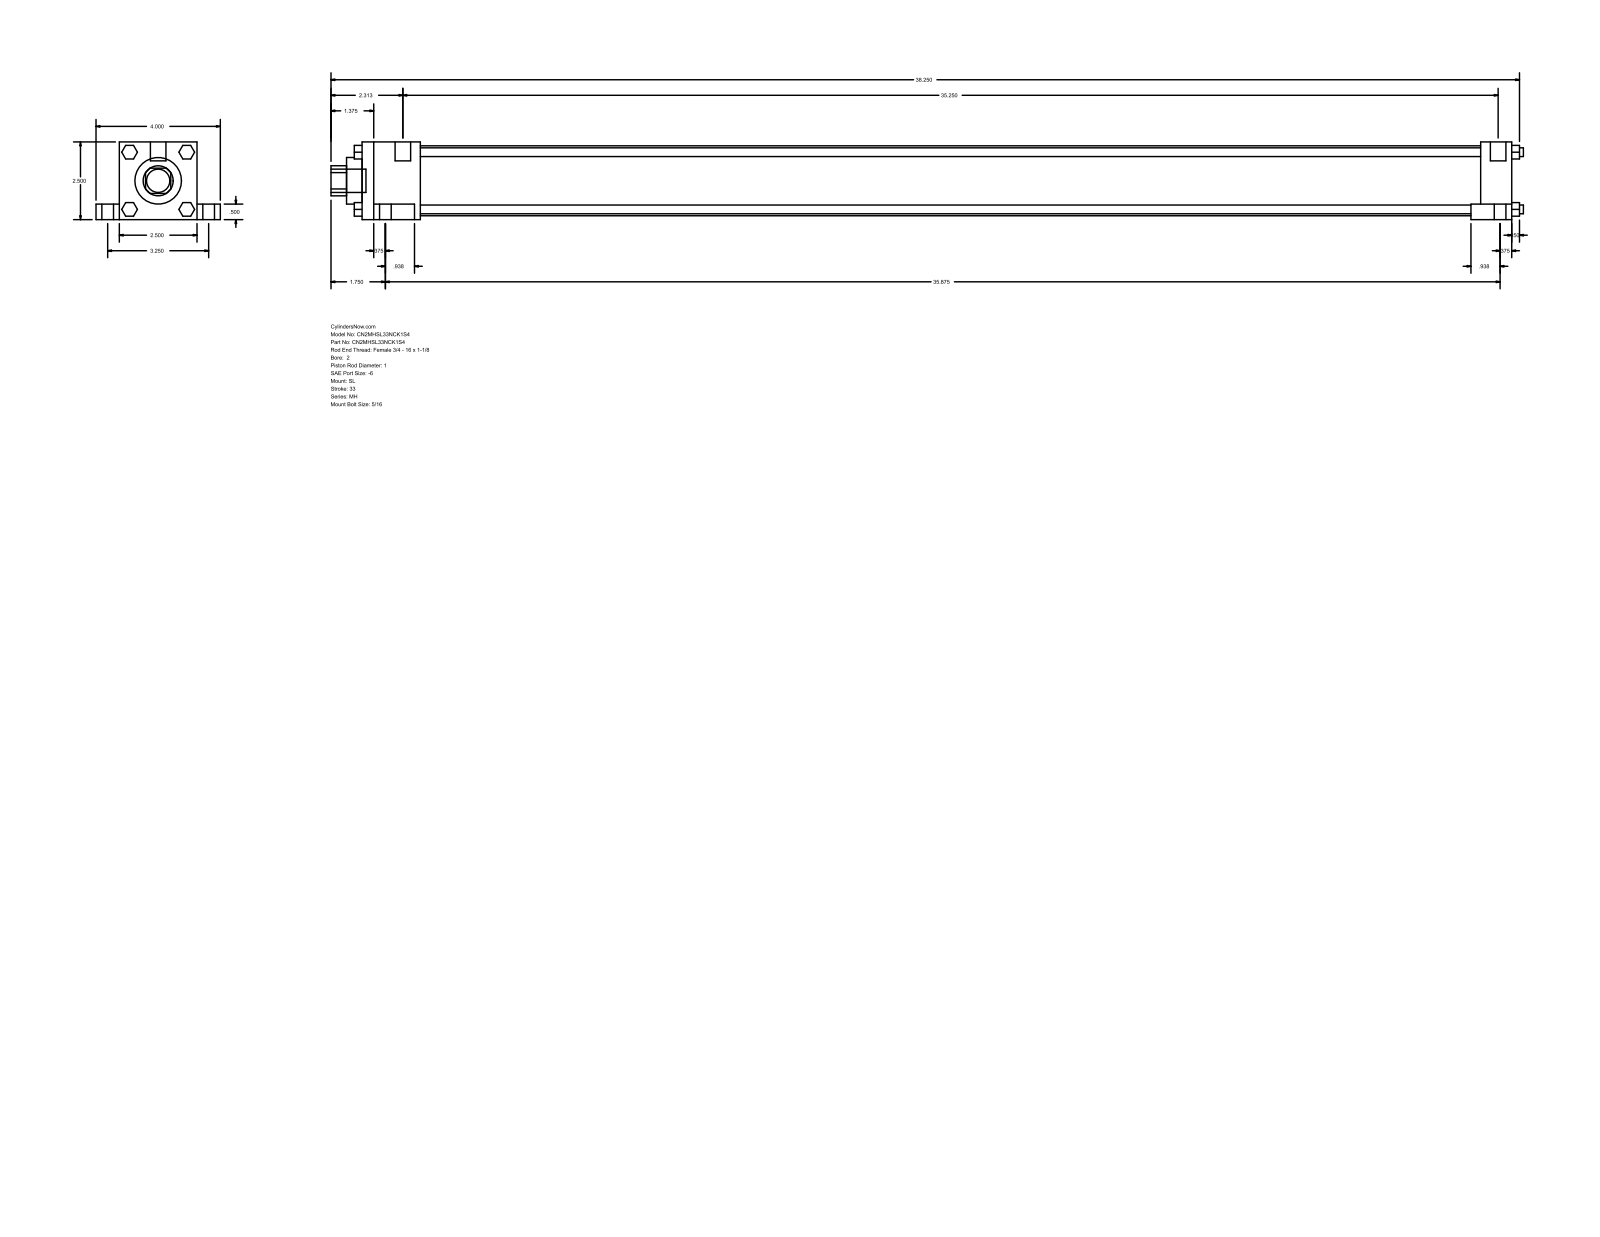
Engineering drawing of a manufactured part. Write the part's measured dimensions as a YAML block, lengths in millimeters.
part_name: "MH_SL__0200_1"
step_written_by: "GSSL Pune (CONFIG_CONTROL_DESIGN)"
units: millimeters
bodies: {solids: 0, faces: 148, planar: 112, cylindrical: 36, other: 0}
overall_size: [974.73, 101.6, 63.5]
round_holes:
  - {diameter: 25.4, count: 1}
  - {diameter: 38.1, count: 1}
  - {diameter: 57.15, count: 1}
round_bosses_or_shafts:
  - {diameter: 15.88, count: 4}
  - {diameter: 9.53, count: 4}
  - {diameter: 7.14, count: 4}
  - {diameter: 5.56, count: 4}
  - {diameter: 12.7, count: 2}
  - {diameter: 19.05, count: 1}
partial_cylinders:
  - {radius: 12.29, count: 1}
face_to_face_distances: [63.5, 939.8, 12.7, 19.05, 50.8, 82.55, 25.4, 9.52, 914.4, 47.63]
